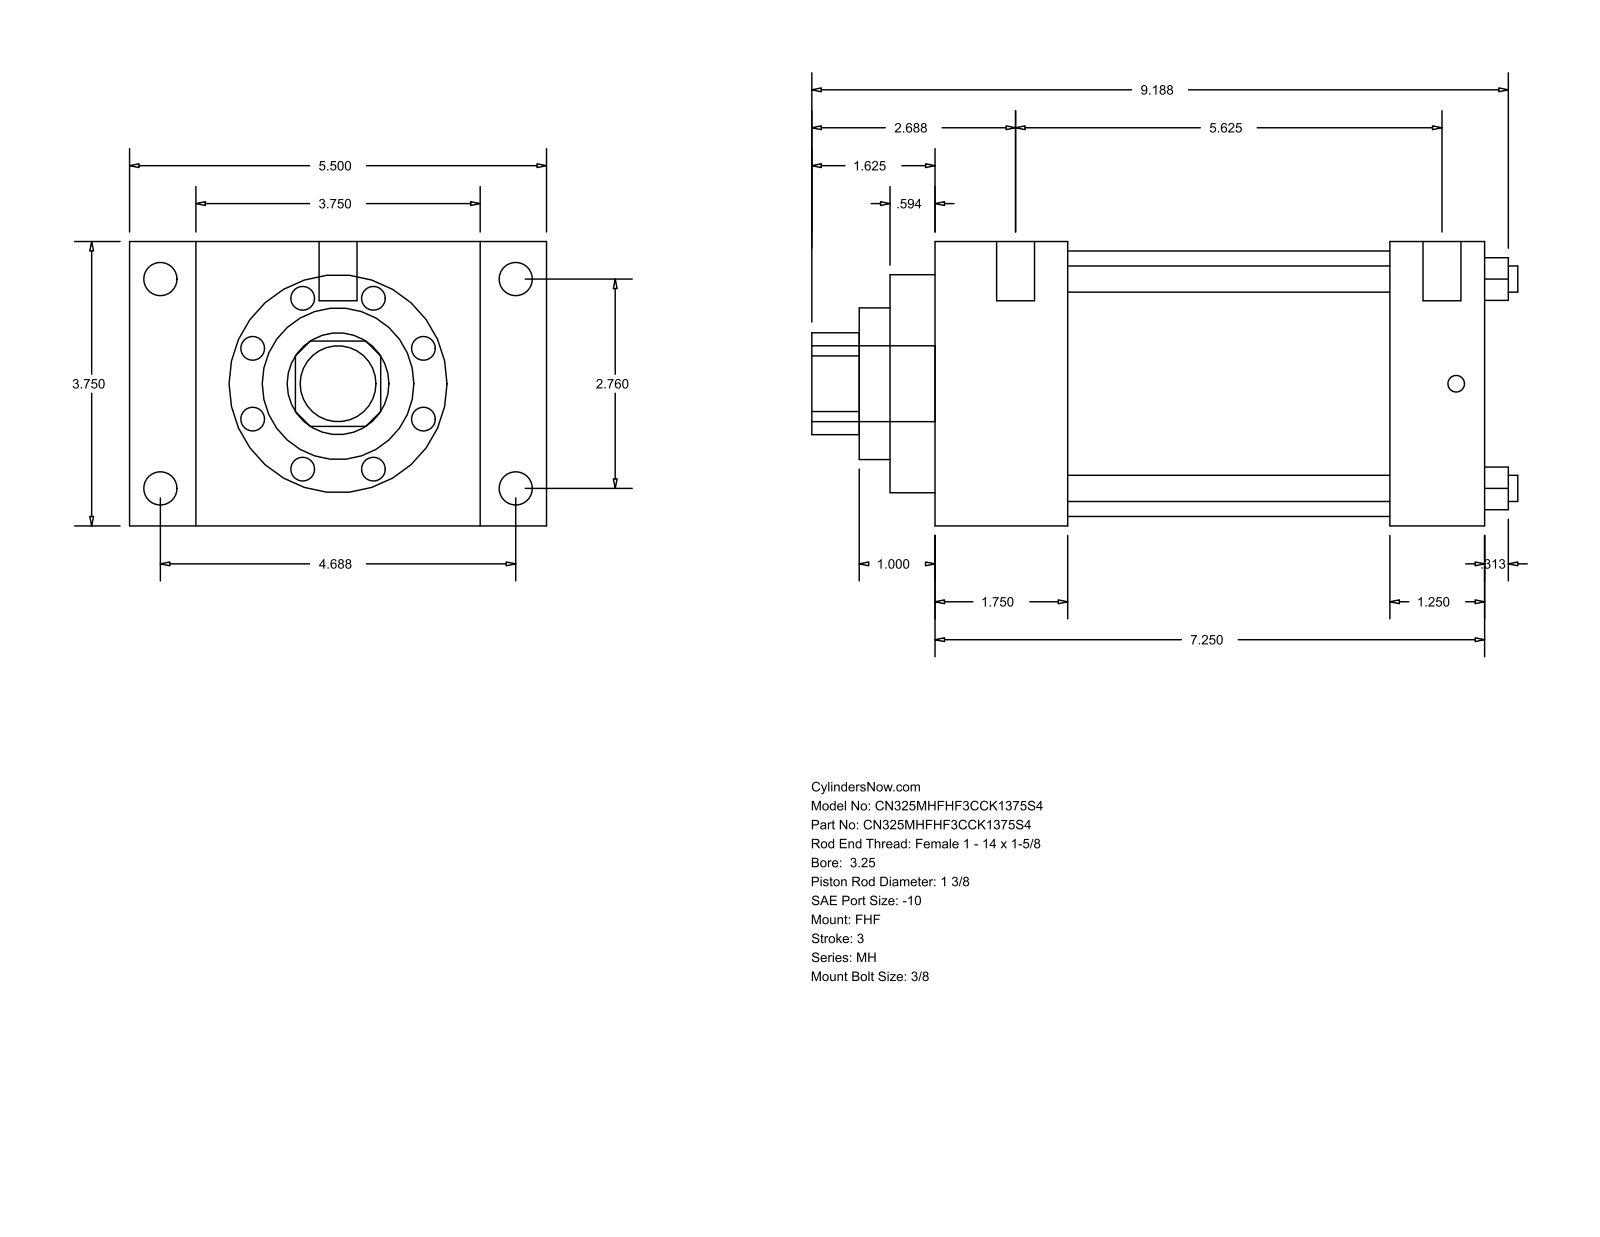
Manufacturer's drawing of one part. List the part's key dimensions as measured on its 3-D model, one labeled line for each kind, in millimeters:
Part name (STEP PRODUCT): MH_FHF__0325_1.375
STEP written by: GSSL Pune (CONFIG_CONTROL_DESIGN)
Units: millimetres
Bodies: 0 solids, 90 faces (61 planar, 29 cylindrical, 0 other)
Overall size (bounding box): 236.54 × 139.7 × 95.25
Round holes (diameter × count): ⌀8.76 ×4, ⌀34.92 ×1, ⌀50.8 ×1, ⌀73.03 ×1, ⌀88.9 ×1
Round bosses / shafts (diameter × count): ⌀11.13 ×4, ⌀5.56 ×4, ⌀12.7 ×2, ⌀25.4 ×1
Partial cylindrical surfaces — rounded edges, fillets, slot ends (radius × count): R17.06 ×1
Main face-to-face distances: 95.24, 184.16, 44.45, 139.71, 22.23, 117.47, 139.7, 152.41, 107.96, 31.75
Hole centre spacings: 49.57, 70.1, 99.14
